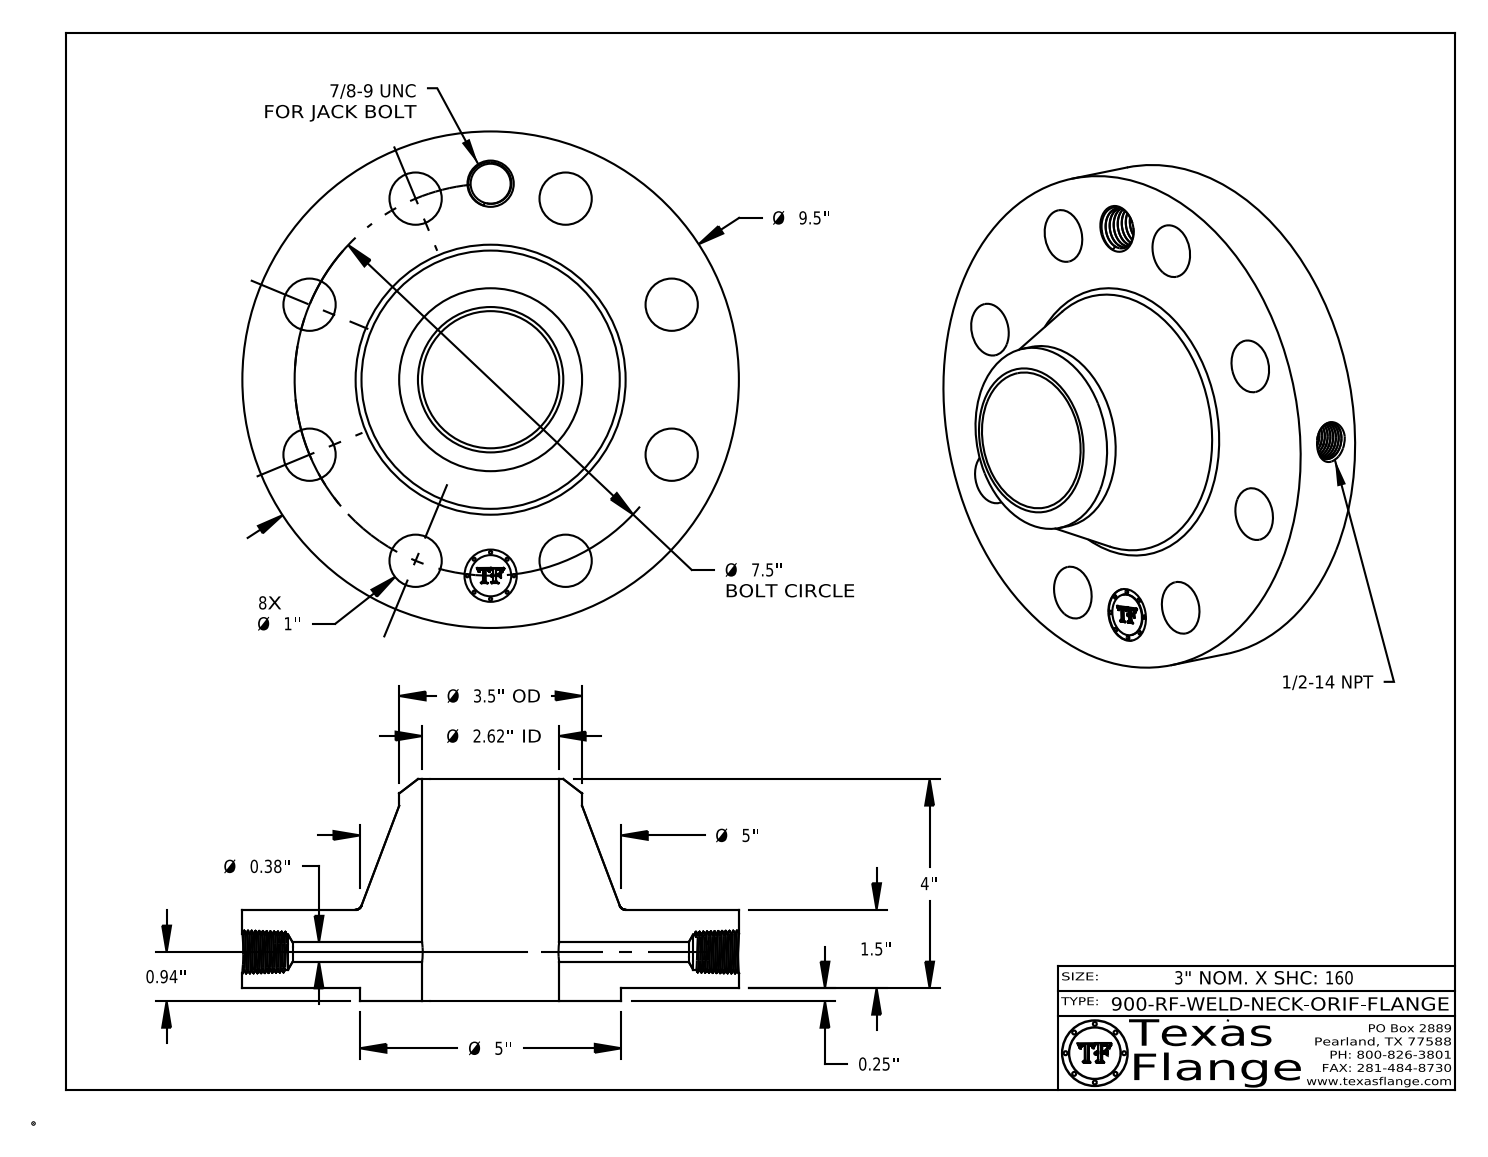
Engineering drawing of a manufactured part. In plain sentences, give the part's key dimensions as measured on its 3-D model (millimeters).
The part is named "900-RF-WELD-NECK". Its 3-D file was written by "CATIA V5 STEP AP214 (AUTOMOTIVE_DESIGN)". It is 1 solid with 759 faces: 369 planar, 90 cylindrical and 300 other. Overall it measures 241.3 by 241.3 by 108 millimeters. Its volume is 1 796 000 cubic millimeters and its surface area 179 500 square millimeters. Round holes: 9 of diameter 25.4, 1 of diameter 9.5, 1 of diameter 17.1, 1 of diameter 19.5, 1 of diameter 66.6. Round bosses or shafts: 8 of diameter 1.5, 1 of diameter 241.3, 1 of diameter 127, 1 of diameter 88.9, 1 of diameter 20. The main face-to-face distances are 38.1, 6.4, 44.5, 108, 101.6, 63.5, 44.1, 37.7, 0.4, 63.9. The hole center spacings are 95.3, 72.9, 134.7, 176, 190.5, 37.2, 105.8, 158.4.
